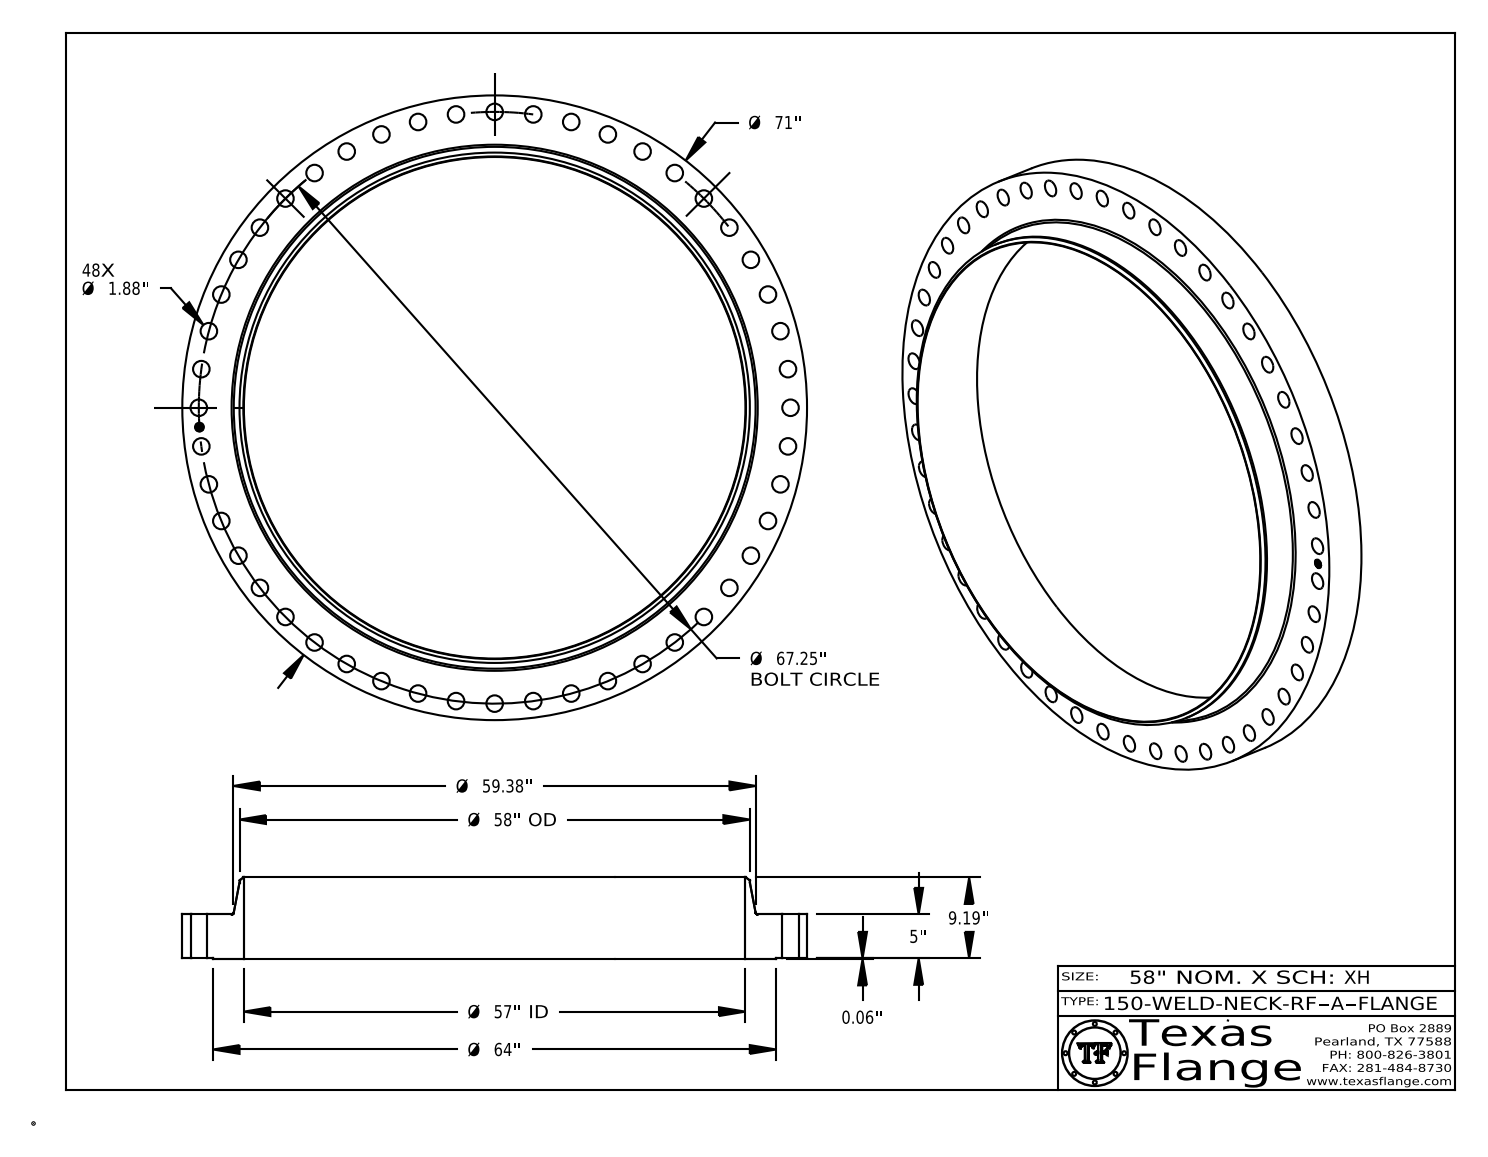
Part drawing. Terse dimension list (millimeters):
name: 150-WELD-NECK-RF, Series A
written by: CATIA V5 STEP AP214 (AUTOMOTIVE_DESIGN)
unit: mm
bodies: 1 solid, 499 faces (369 planar, 124 cylindrical, 6 other)
size: 1803.4 × 1803.4 × 235
volume: 114 900 000 mm³; area: 4 745 000 mm²
holes: 48× ⌀47.8, 1× ⌀25.4, 1× ⌀1447.8
bosses: 8× ⌀1.5, 1× ⌀1803.4, 1× ⌀1625.6, 1× ⌀1473.2, 1× ⌀20
face distances: 128.6, 1.6, 127, 235, 233.4, 106.4, 0.4, 128.2, 126.6, 106.8
hole spacings: 854.1, 223, 111.7, 1704.5, 442.1, 653.7, 333.2, 854.1
